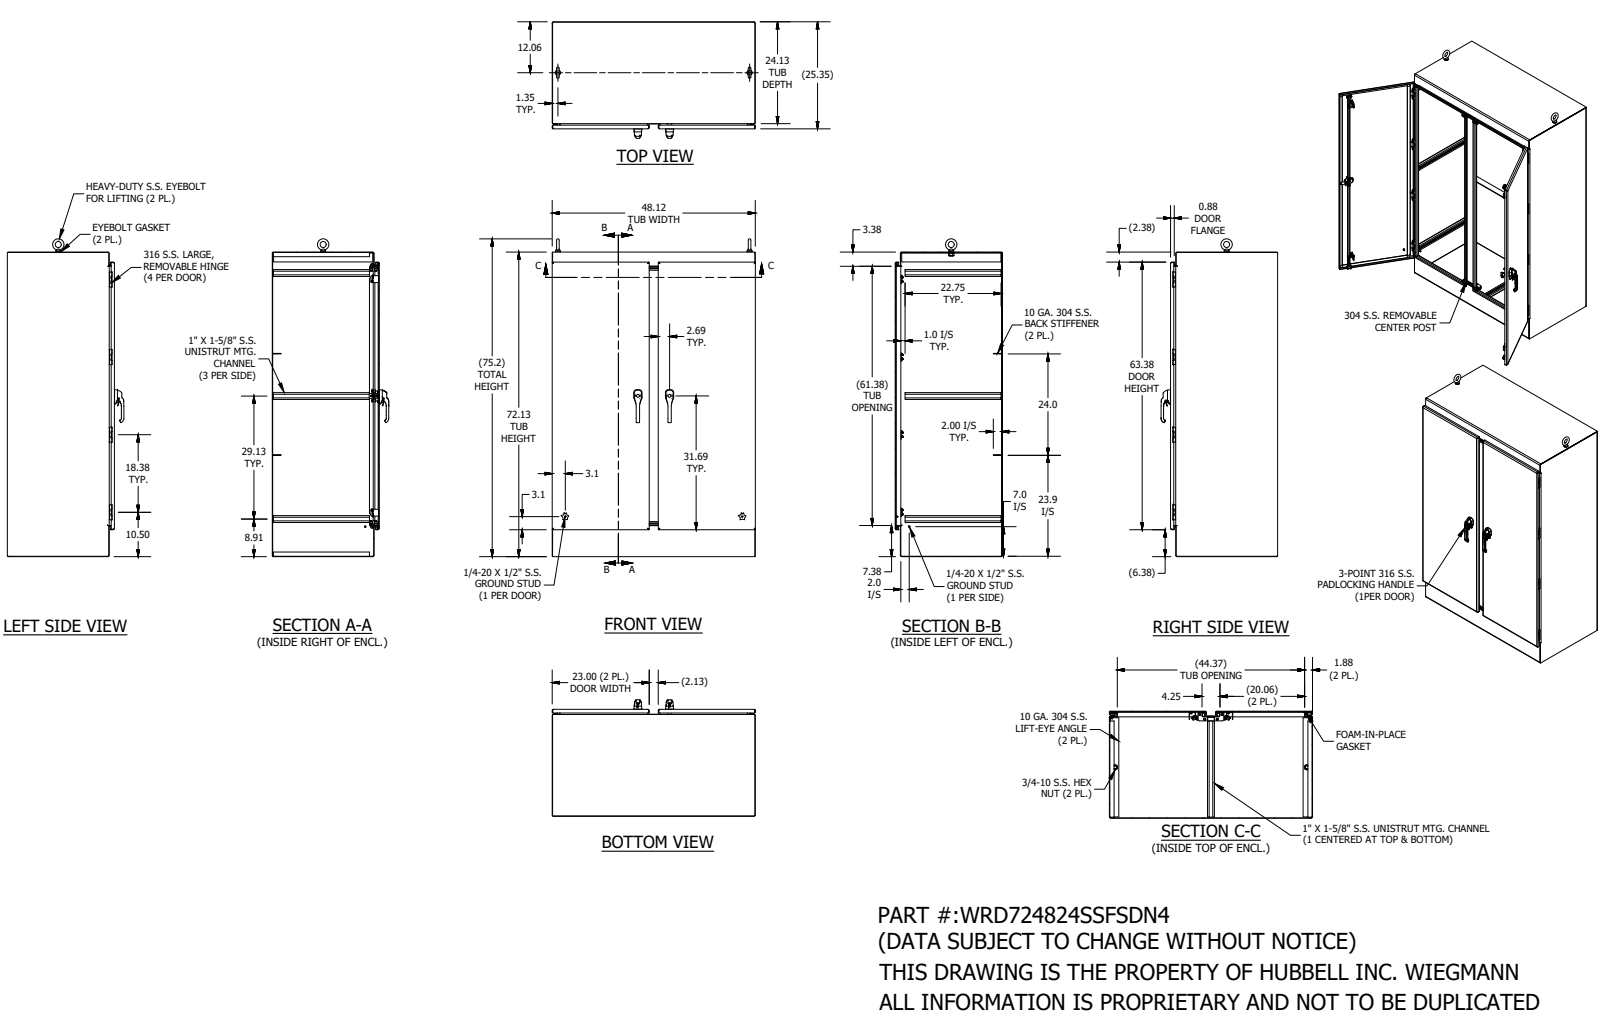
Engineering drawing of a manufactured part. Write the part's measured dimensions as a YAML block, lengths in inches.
part_name: "WRD724824SSFSDN4; WRD724824SSFSDN4BLR; WRD4824SSFSDN4TOP; WRD4824SSFSDN4BTM (+8 more)"
step_written_by: "Autodesk Inventor 2018 (AUTOMOTIVE_DESIGN)"
units: inches
bodies: {solids: 227, faces: 9194, planar: 3894, cylindrical: 3238, other: 2062}
overall_size: [75.248, 48.133, 27.598]
volume: 1748
surface_area: 32270
round_holes:
  - {diameter: 0.14, count: 48}
  - {diameter: 0.266, count: 20}
  - {diameter: 0.195, count: 16}
  - {diameter: 0.294, count: 16}
  - {diameter: 0.65, count: 16}
  - {diameter: 0.136, count: 8}
  - {diameter: 0.164, count: 8}
  - {diameter: 0.187, count: 8}
  - {diameter: 0.201, count: 8}
  - {diameter: 0.262, count: 8}
  - {diameter: 0.213, count: 6}
  - {diameter: 0.281, count: 6}
round_bosses_or_shafts:
  - {diameter: 0.25, count: 33}
  - {diameter: 0.625, count: 16}
  - {diameter: 0.182, count: 16}
  - {diameter: 0.237, count: 8}
  - {diameter: 0.236, count: 6}
  - {diameter: 1, count: 4}
  - {diameter: 0.563, count: 4}
  - {diameter: 0.531, count: 4}
partial_cylinders:
  - {radius: 0.02, count: 344}
  - {radius: 0.012, count: 229}
  - {radius: 0.062, count: 64}
  - {radius: 0.125, count: 58}
  - {radius: 0.019, count: 42}
  - {radius: 0.079, count: 28}
  - {radius: 0.05, count: 26}
  - {radius: 0.039, count: 22}
face_to_face_distances: [0.104, 48.021, 25.245, 25.141, 0.104, 25.349, 25.245, 72.021, 47.917, 24.021]
hole_center_spacings: [8.841, 0.018, 50.348, 0.023, 0.029, 1, 18.375, 36.75]
